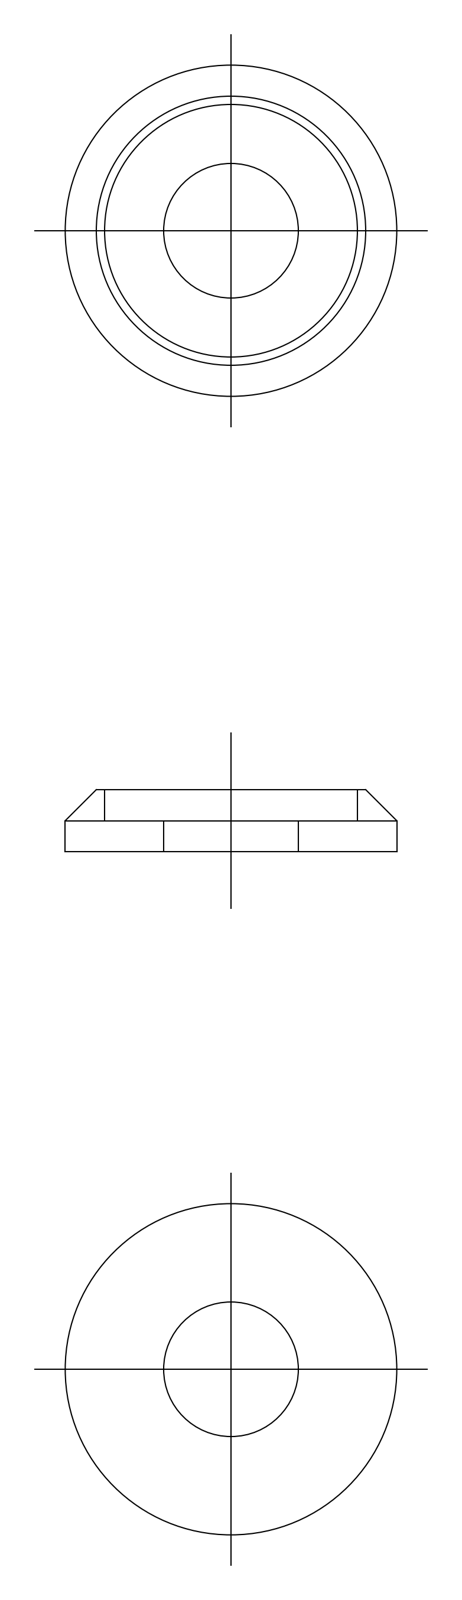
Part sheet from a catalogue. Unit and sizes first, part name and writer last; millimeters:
Units: millimetres
Overall size (bounding box): 16 × 16 × 3
Volume: 326 mm³ · Surface area: 528 mm²
Bodies: 1 solid, 11 faces (0 planar, 0 cylindrical, 11 other)
Part name (STEP PRODUCT): facing ring
STEP written by: CADfix (AUTOMOTIVE_DESIGN)
